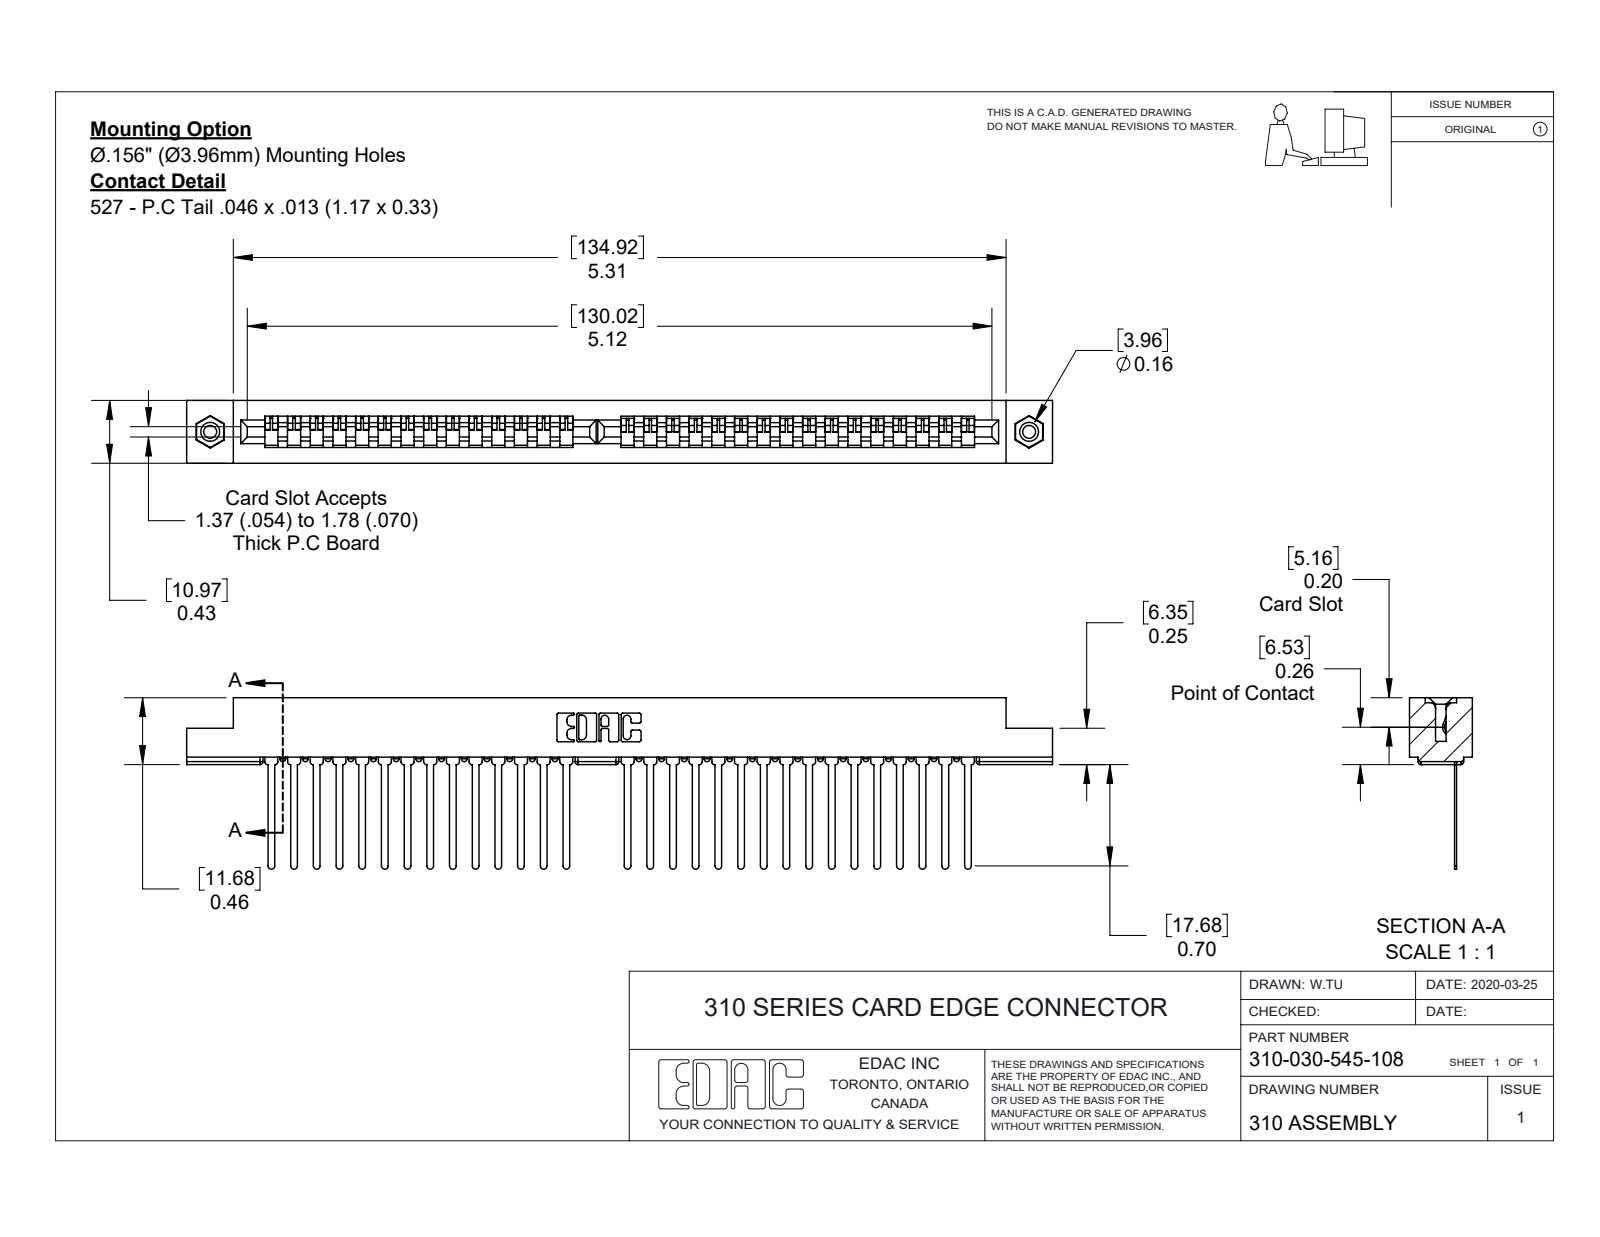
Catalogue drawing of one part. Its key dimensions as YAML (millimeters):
part_name: "310 Part_.116 Hex; 310-030-545-108; 345-250-001_345-250-003-102; 307-290-001_545"
step_written_by: "SolidWorks 2016 (CONFIG_CONTROL_DESIGN)"
units: millimeters
bodies: {solids: 33, faces: 1906, planar: 1226, cylindrical: 600, other: 80}
overall_size: [151.21, 29.95, 10.97]
volume: 12784
surface_area: 15983
round_holes:
  - {diameter: 2.26, count: 2}
  - {diameter: 3.17, count: 2}
  - {diameter: 3.96, count: 2}
round_bosses_or_shafts:
  - {diameter: 3.94, count: 2}
partial_cylinders:
  - {radius: 0.51, count: 158}
  - {radius: 0.58, count: 30}
  - {radius: 0.25, count: 22}
  - {radius: 0.17, count: 6}
  - {radius: 0.8, count: 6}
  - {radius: 0.67, count: 3}
  - {radius: 0.3, count: 2}
  - {radius: 0.64, count: 2}
face_to_face_distances: [2.76, 8.22, 0.38, 0.33, 10.98, 1.82, 3.14, 7.84, 5.08, 4.75]
hole_center_spacings: [143]
